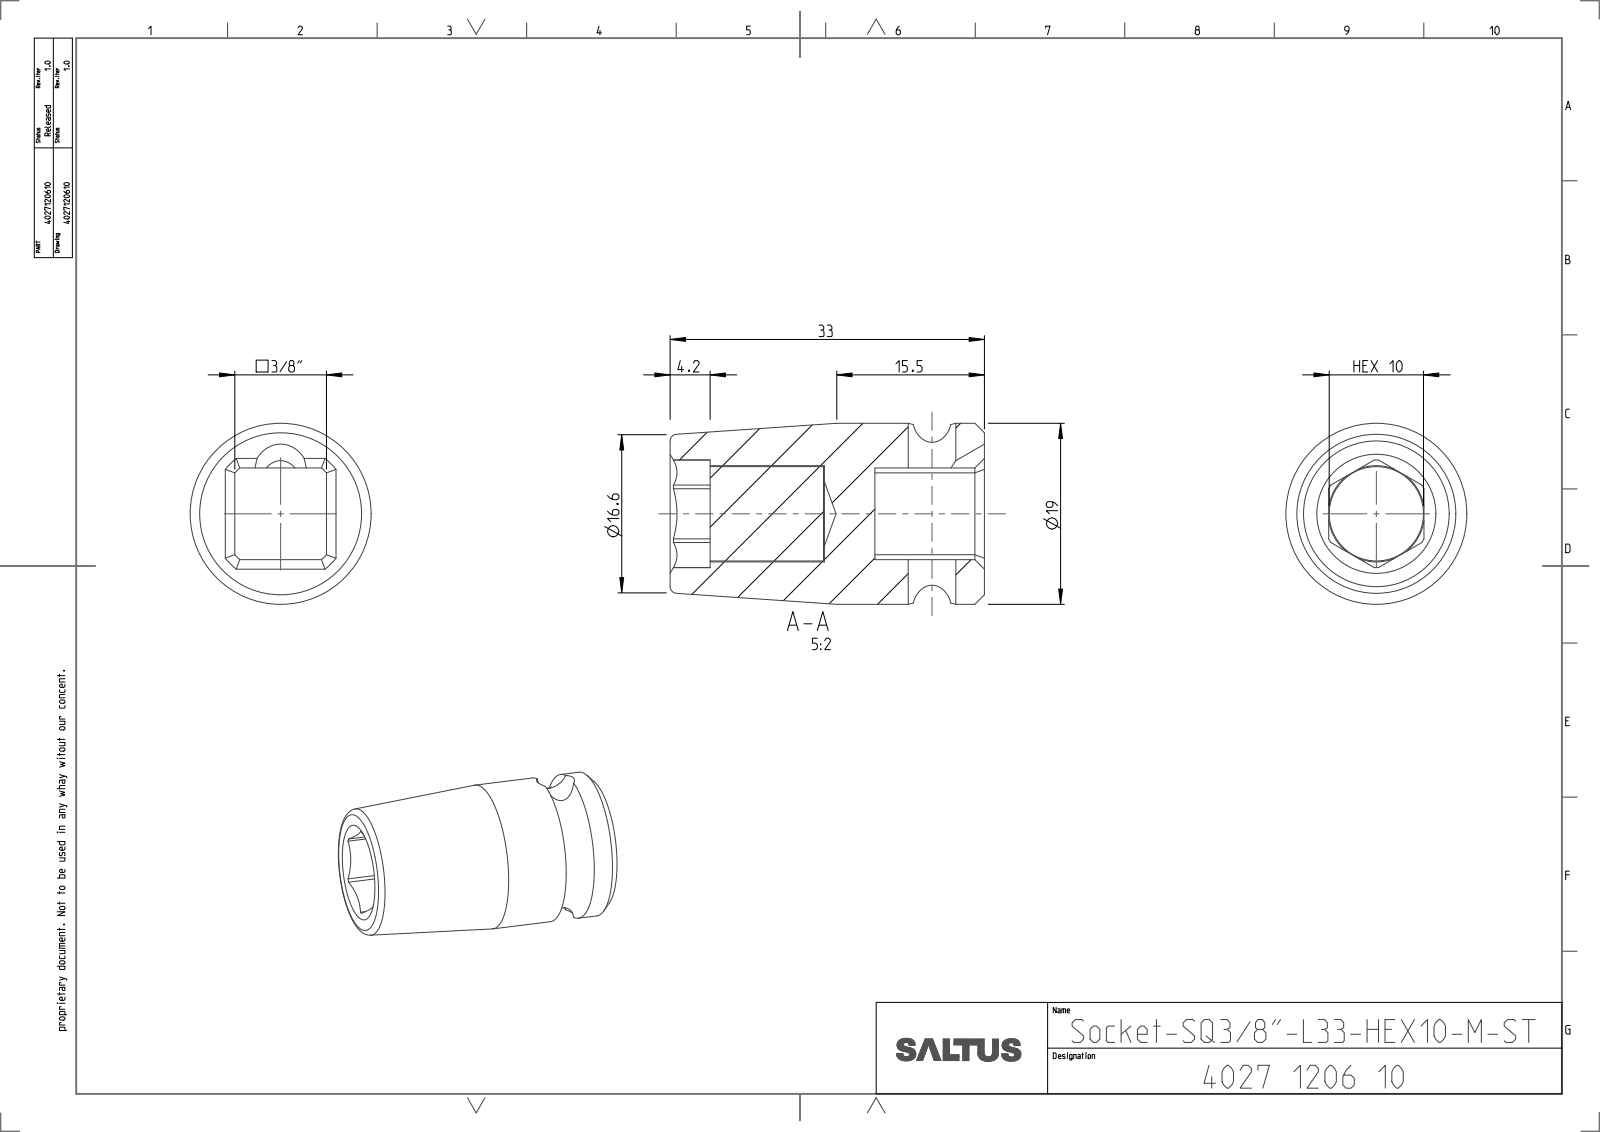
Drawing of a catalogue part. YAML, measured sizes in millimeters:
part_name: "4027120610"
step_written_by: "CREO PARAMETRIC BY PTC INC, 2022414 (CONFIG_CONTROL_DESIGN)"
units: millimeters
bodies: {solids: 2, faces: 72, planar: 33, cylindrical: 23, other: 16}
overall_size: [33, 19, 19]
volume: 6797
surface_area: 3886
round_holes:
  - {diameter: 5, count: 1}
  - {diameter: 10.1, count: 1}
round_bosses_or_shafts:
  - {diameter: 19, count: 1}
  - {diameter: 9.9, count: 1}
partial_cylinders:
  - {radius: 3, count: 1}
  - {radius: 5.65, count: 1}
  - {radius: 6.45, count: 1}
face_to_face_distances: [9.62, 11.5, 28.8, 17.3, 16.9, 5.4, 11.9, 33, 21.5, 16.1]
